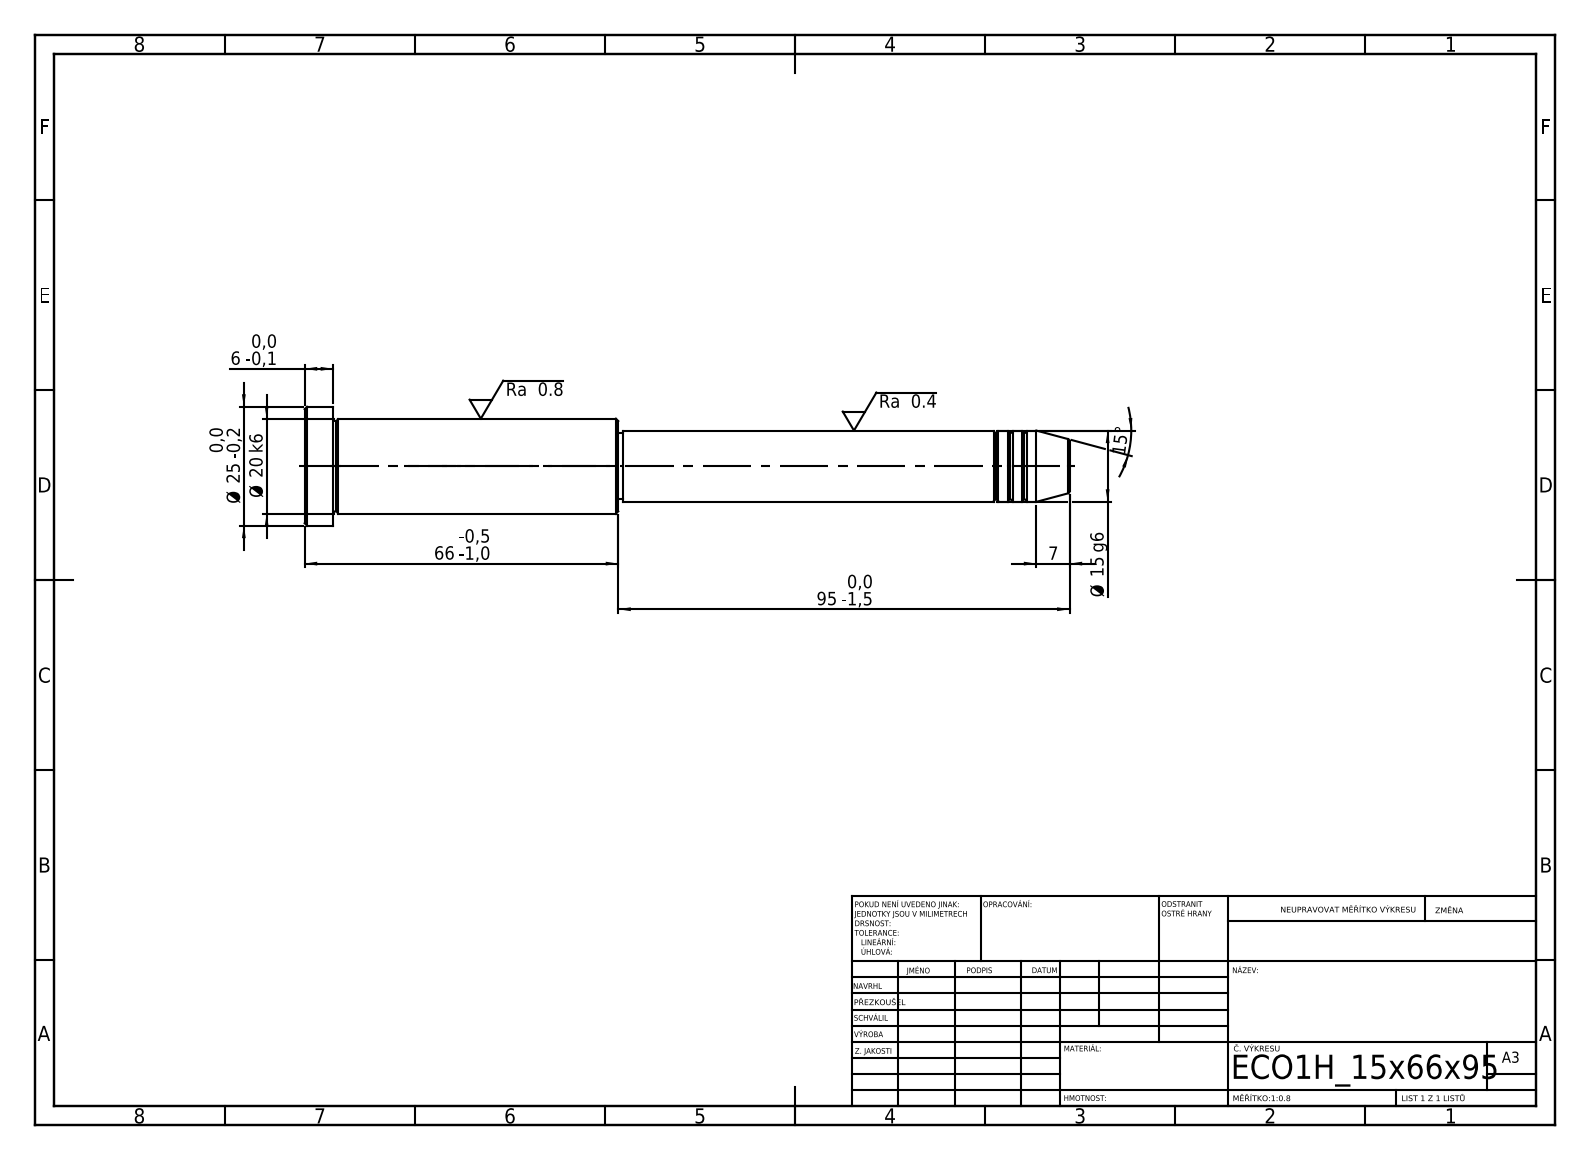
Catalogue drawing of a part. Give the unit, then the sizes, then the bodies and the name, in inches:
Units: inches
Overall size (bounding box): 6.339 × 0.984 × 0.984
Round bosses / shafts (diameter × count): ⌀0.984 ×1, ⌀0.787 ×1, ⌀0.591 ×1, ⌀0.551 ×1
Main face-to-face distances: 0.236, 2.362, 2.598, 3.74, 6.102, 6.339, 3.701, 0.039, 2.402, 2.638
Volume: 2.33 in³ · Surface area: 15.02 in²
Bodies: 1 solid, 43 faces (5 planar, 14 cylindrical, 24 other)
STEP written by: SolidWorks 2019 (CONFIG_CONTROL_DESIGN)
